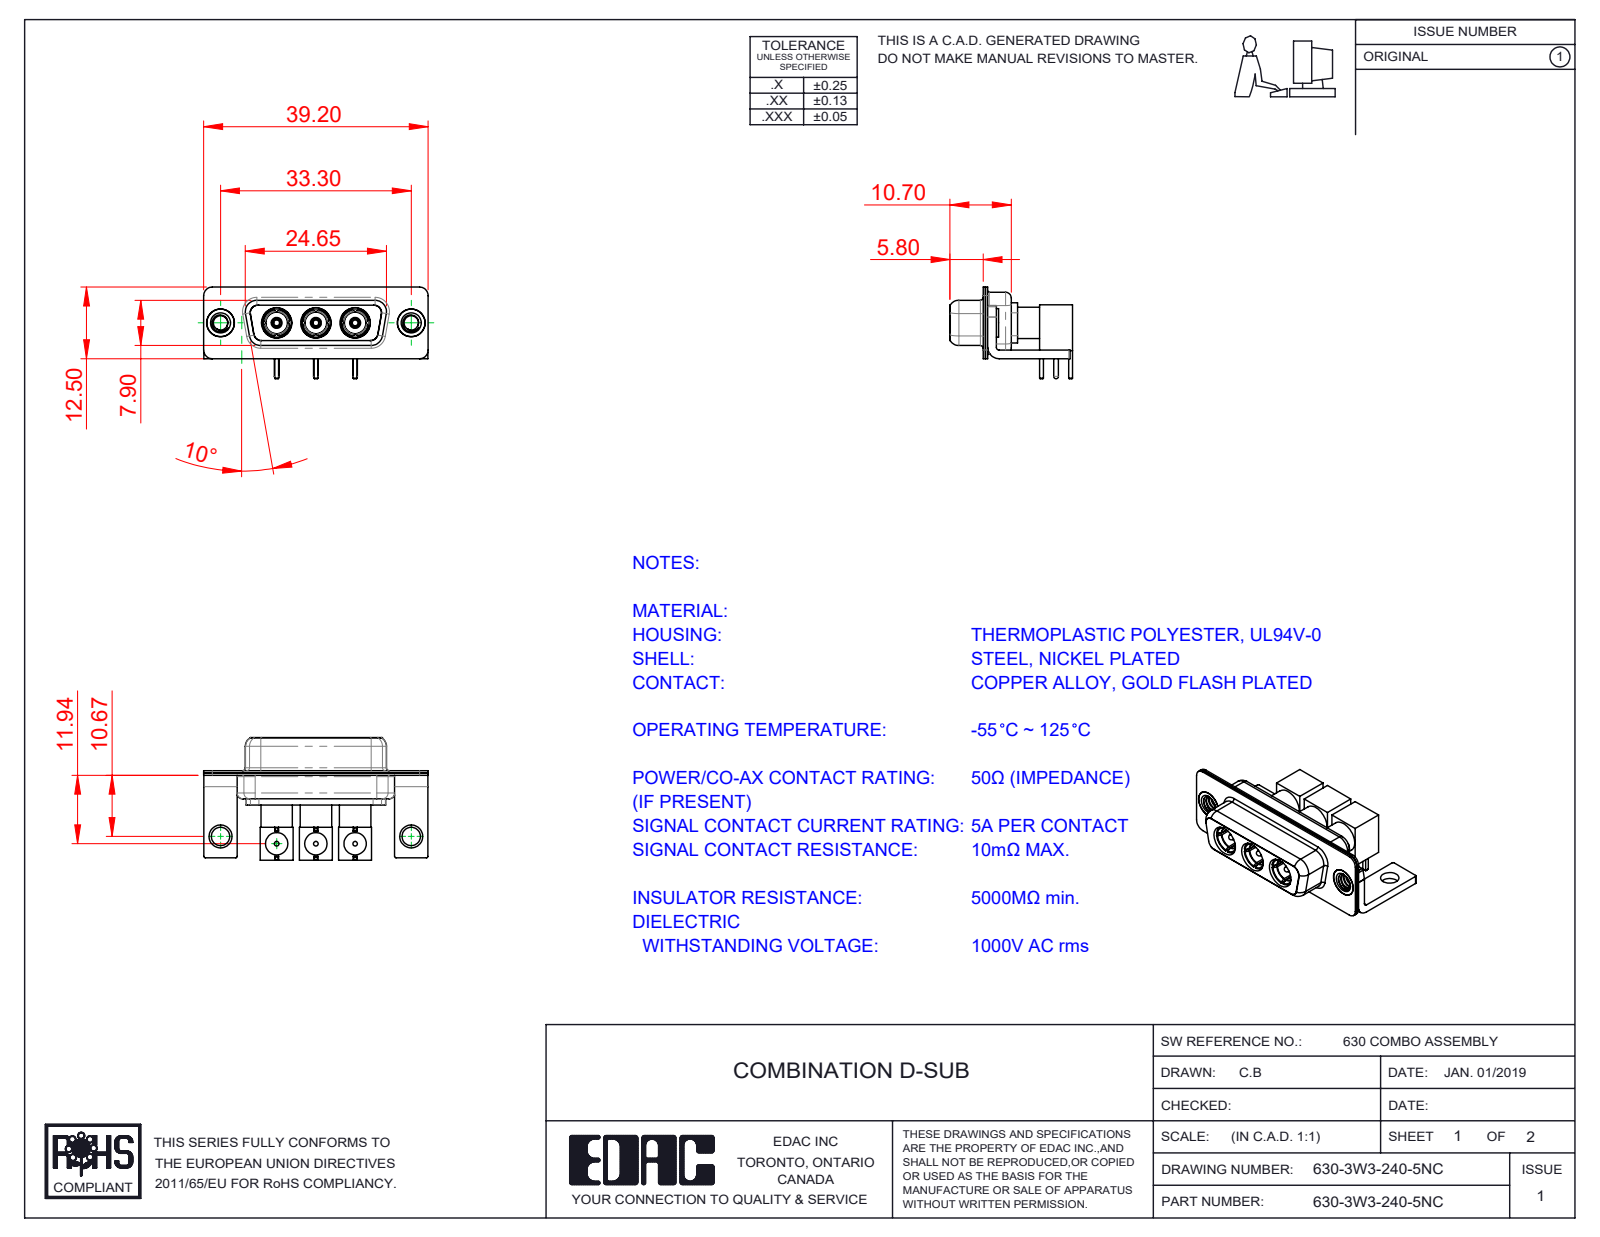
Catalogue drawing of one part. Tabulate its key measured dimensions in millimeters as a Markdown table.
| quantity | value |
| --- | --- |
| part name | 630Combo Shell Front_15 Contacts; Co-Ax Plug Assy_RA; 630Combo Shell Rear_15 Contacts; Co-Ax Plug_RA PC Tail (+8 more) |
| STEP written by | SolidWorks 2020 (CONFIG_CONTROL_DESIGN) |
| units | millimeters |
| bodies | 25 solids, 821 faces (288 planar, 350 cylindrical, 183 other) |
| overall size | 39.2 × 21.41 × 16 |
| volume | 3 402 mm³ |
| surface area | 8 377 mm² |
| round holes (diameter × count) | 4.85 × 5, 0.8 × 3, 1.1 × 3, 1.5 × 3, 2.83 × 3, 3.1 × 3, 3.3 × 3, 3.9 × 3, 3.92 × 3, 4.1 × 3, 5.3 × 3, 2.5 × 2 |
| round bosses / shafts (diameter × count) | 5 × 5, 5.5 × 3, 5.2 × 3, 4.75 × 3, 4.15 × 3, 4 × 3, 3.76 × 3, 3.75 × 3 |
| partial cylindrical surfaces (radius × count) | 0.25 × 16, 1.5 × 16, 2 × 13, 1.35 × 12, 1.6 × 8, 0.5 × 5, 0.6 × 4, 0.65 × 4 |
| main face-to-face distances | 0.4, 1.4, 0.8, 1.8, 0.45, 8.45, 8.9, 1.85, 1.5, 6.2 |
| hole center spacings | 6.85, 9.8, 9.88, 13.7, 16.65, 16.7, 23.5, 23.53 |
